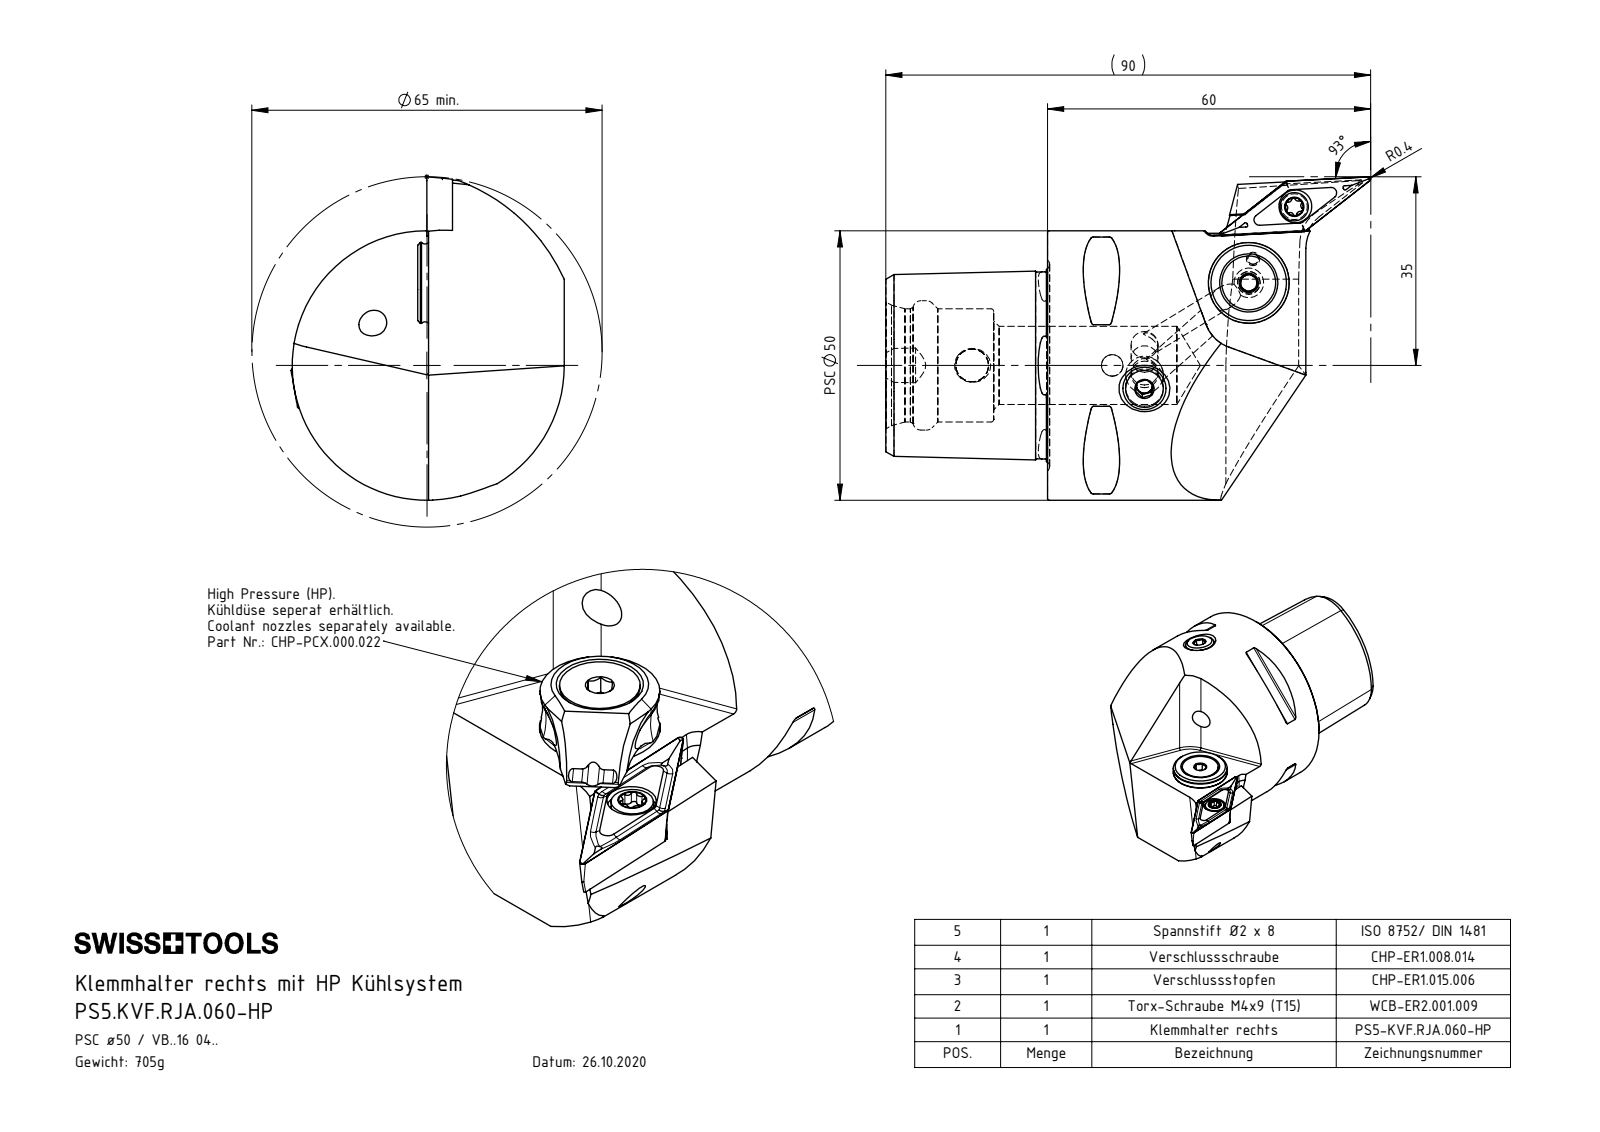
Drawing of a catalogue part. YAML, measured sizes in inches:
part_name: "CHP-ER1.008.014_A; PS5.KVF.RJA.060-HP; CHP-ER1.015.006; CHP-ER1.015.006_A (+6 more)"
step_written_by: "SolidWorks 2017 (AUTOMOTIVE_DESIGN)"
units: inches
bodies: {solids: 8, faces: 276, planar: 94, cylindrical: 64, other: 118}
overall_size: [3.543, 2.362, 1.997]
volume: 5.473
surface_area: 33.42
round_holes:
  - {diameter: 0.165, count: 2}
  - {diameter: 0.197, count: 2}
  - {diameter: 0.24, count: 2}
  - {diameter: 0.047, count: 1}
  - {diameter: 0.079, count: 1}
  - {diameter: 0.098, count: 1}
  - {diameter: 0.118, count: 1}
  - {diameter: 0.13, count: 1}
  - {diameter: 0.157, count: 1}
  - {diameter: 0.173, count: 1}
  - {diameter: 0.205, count: 1}
  - {diameter: 0.276, count: 1}
round_bosses_or_shafts:
  - {diameter: 1.969, count: 1}
  - {diameter: 0.591, count: 1}
  - {diameter: 0.528, count: 1}
  - {diameter: 0.394, count: 1}
  - {diameter: 0.315, count: 1}
  - {diameter: 0.217, count: 1}
  - {diameter: 0.207, count: 1}
  - {diameter: 0.197, count: 1}
partial_cylinders:
  - {radius: 0.02, count: 10}
  - {radius: 0.013, count: 6}
  - {radius: 0.023, count: 6}
  - {radius: 0.006, count: 2}
  - {radius: 0.276, count: 2}
  - {radius: 0.069, count: 1}
  - {radius: 0.157, count: 1}
  - {radius: 1.004, count: 1}
face_to_face_distances: [1.181, 0.177, 0.176, 0.815, 0.817, 0.992, 0.755, 1.748, 0.787, 0.394]
hole_center_spacings: [0.177, 0.487, 0.494, 0.648, 0.655, 1.024, 1.167, 1.29]
